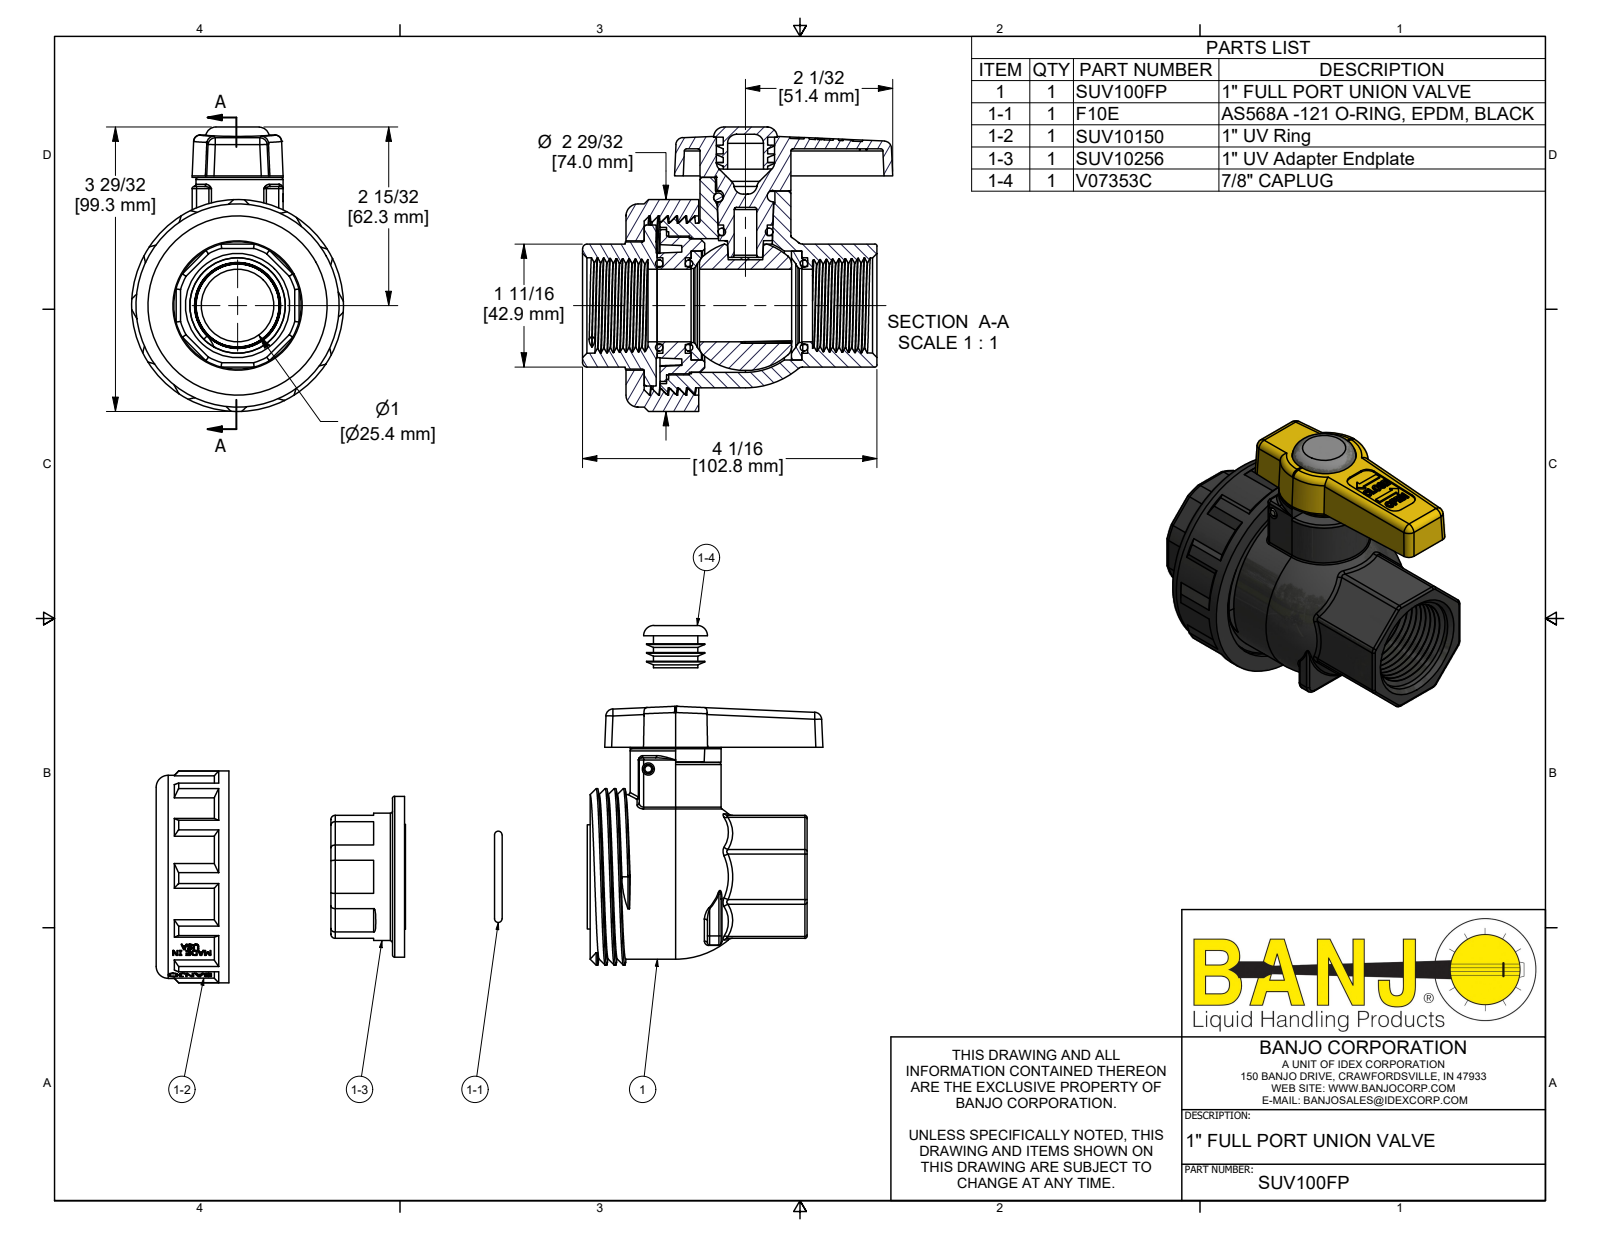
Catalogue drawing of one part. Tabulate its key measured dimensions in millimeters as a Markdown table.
| quantity | value |
| --- | --- |
| part name | SUV100FP; SUV10254; UV10257; V10258B (+8 more) |
| STEP written by | Autodesk Inventor 2022 (AUTOMOTIVE_DESIGN) |
| units | millimeters |
| bodies | 14 solids, 977 faces (413 planar, 180 cylindrical, 384 other) |
| overall size | 108.3 × 99.3 × 74 |
| volume | 198 400 mm³ |
| surface area | 98 190 mm² |
| round holes (diameter × count) | 3.3 × 1, 8 × 1, 12.5 × 1, 20.4 × 1, 20.6 × 1, 22.4 × 1, 25.4 × 1, 25.9 × 1, 27.8 × 1, 33.4 × 1, 38.1 × 1, 45.2 × 1 |
| round bosses / shafts (diameter × count) | 74 × 1, 70.9 × 1, 61.7 × 1, 57.5 × 1, 56.2 × 1, 53.1 × 1, 48.5 × 1, 46.6 × 1 |
| partial cylindrical surfaces (radius × count) | 0.8 × 26, 1.5 × 13, 2.5 × 10, 2.3 × 8, 3.2 × 6, 16.5 × 4, 9.4 × 1, 9.6 × 1 |
| main face-to-face distances | 42.9, 6.4, 10.5, 4.2, 13.5, 25.4, 19.1, 14.9, 7.8, 2 |
